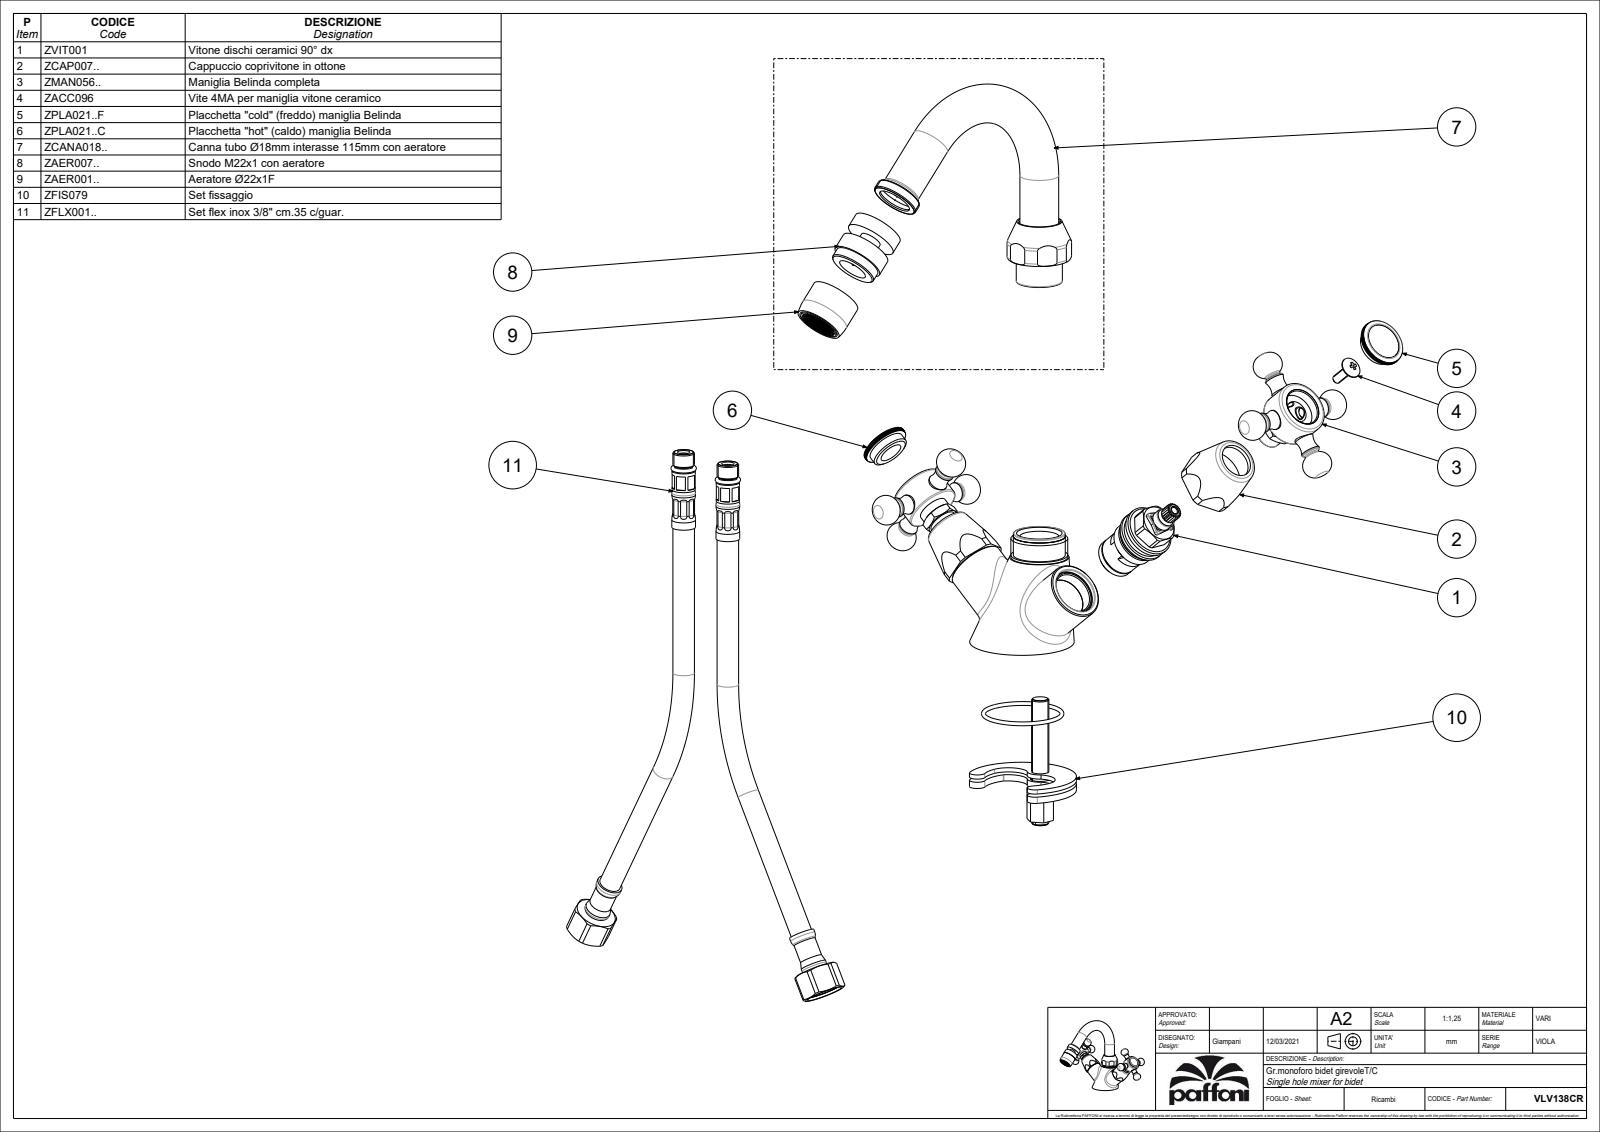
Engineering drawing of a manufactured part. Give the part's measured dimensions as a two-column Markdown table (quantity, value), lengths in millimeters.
| quantity | value |
| --- | --- |
| part name | VLV138CR |
| STEP written by | CREO PARAMETRIC BY PTC INC, 2020044 (CONFIG_CONTROL_DESIGN) |
| units | millimeters |
| bodies | 1 solid, 1235 faces (567 planar, 400 cylindrical, 268 other) |
| overall size | 175.57 × 147.23 × 132.5 |
| volume | 146 736 mm³ |
| surface area | 50 570 mm² |
| round holes (diameter × count) | 9 × 4, 11 × 2, 15.7 × 2, 18 × 2, 19 × 2, 21 × 2, 21.5 × 2, 23 × 2, 6 × 1, 6.8 × 1, 12.6 × 1, 16.4 × 1 |
| round bosses / shafts (diameter × count) | 9 × 6, 7 × 6, 26.3 × 2, 25 × 2, 18 × 2, 14 × 2, 13 × 2, 34 × 1 |
| partial cylindrical surfaces (radius × count) | 3.5 × 2, 11 × 2, 14.5 × 2, 15 × 1 |
| main face-to-face distances | 35.21, 22, 57.21, 26.49, 5, 24.01, 28.5, 23.7, 28.7, 46.01 |
| hole center spacings | 7, 13.38, 13.89, 0.6, 11.4, 12, 14 |
